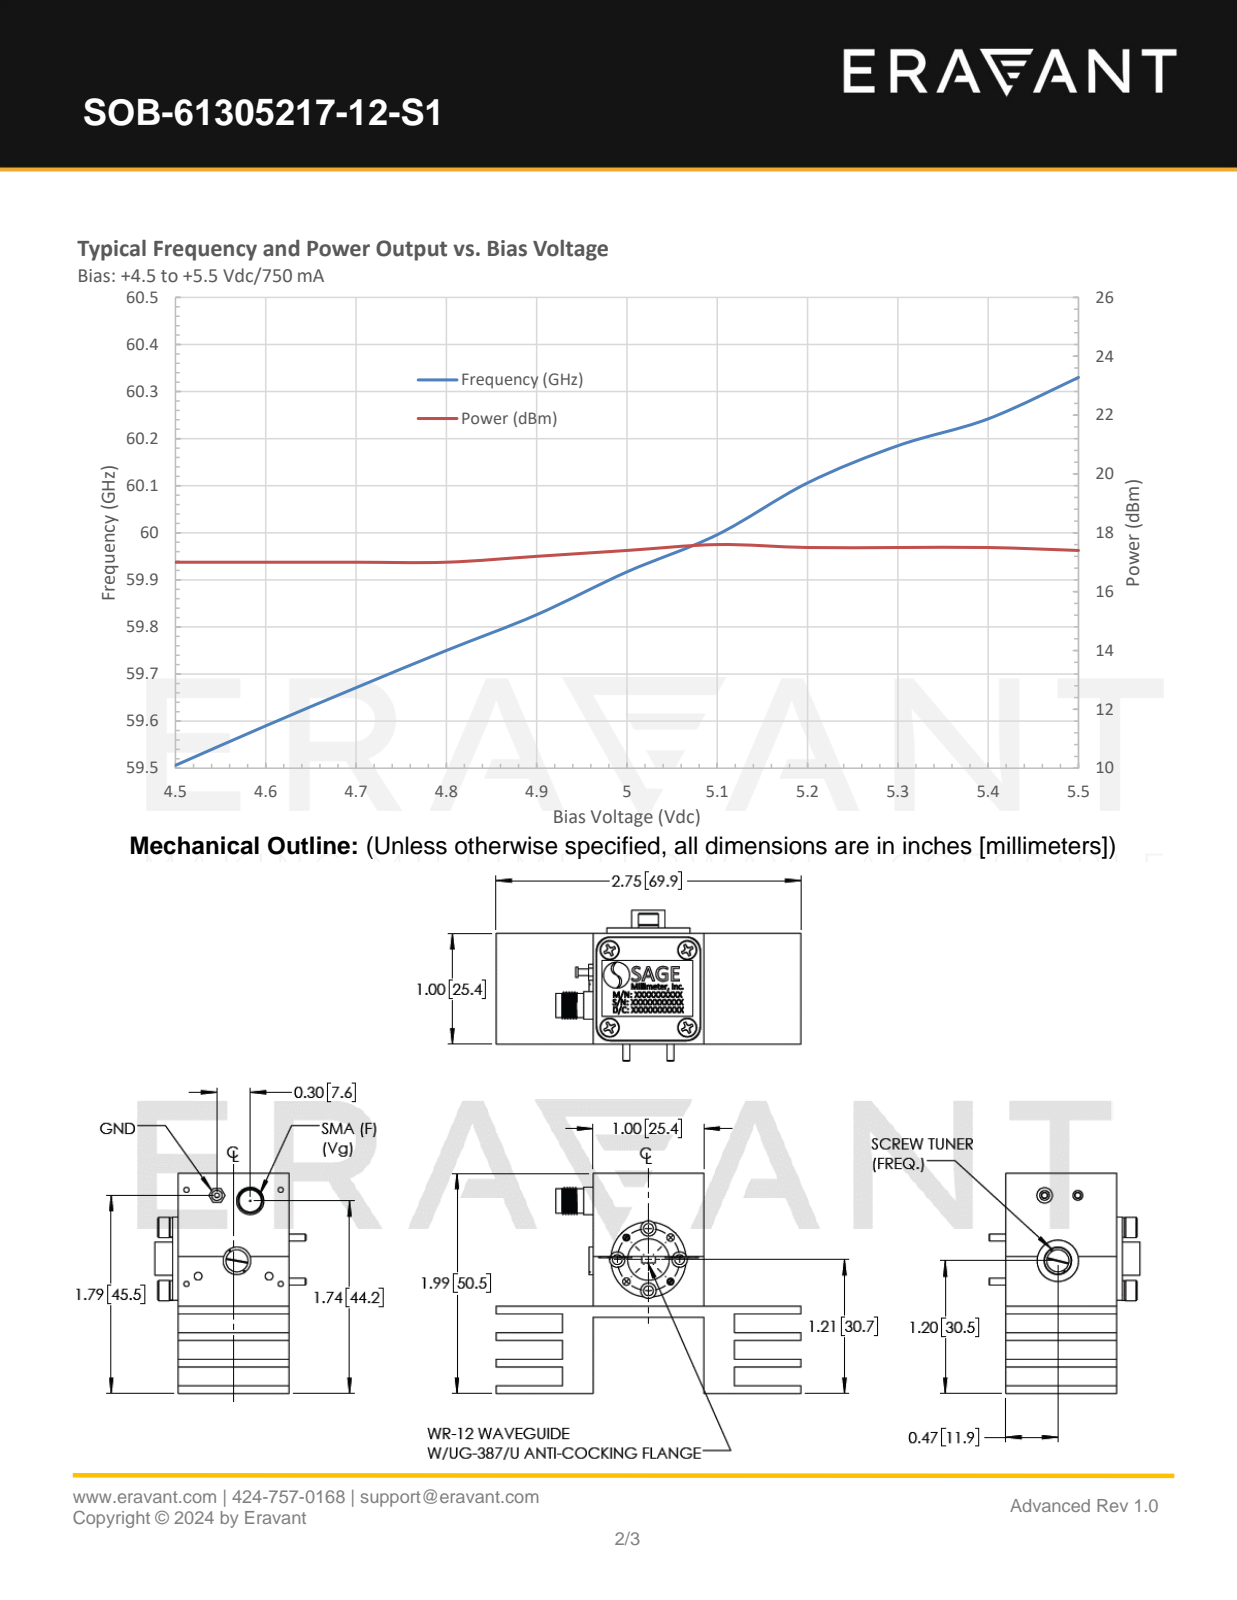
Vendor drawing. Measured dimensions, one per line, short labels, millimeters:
name: OM-SE-A-C, DF
written by: SolidWorks 2021 (AUTOMOTIVE_DESIGN)
unit: mm
bodies: 27 solids, 1301 faces (363 planar, 620 cylindrical, 318 other)
size: 69.9 × 50.5 × 34.6
volume: 30 660 mm³; area: 24 940 mm²
holes: 18× ⌀2.3, 8× ⌀1.5, 7× ⌀3, 6× ⌀1.6, 6× ⌀1.8, 6× ⌀3.6, 4× ⌀1.2, 4× ⌀4.8, 2× ⌀1.7, 2× ⌀3.3, 1× ⌀0.4, 1× ⌀0.6
bosses: 6× ⌀2.2, 5× ⌀2.8, 4× ⌀1.9, 3× ⌀4.6, 3× ⌀2, 2× ⌀4.4, 2× ⌀1.6, 1× ⌀19.1
rounds: 8× R3.2, 4× R1.4, 2× R0.9, 2× R1.1, 2× R1.5, 1× R10.3
face distances: 6.1, 25.4, 1.8, 4.3, 12.2, 14, 7.9, 6.1, 18.3, 16.5
hole spacings: 7.1, 5.5, 10.1, 10.3, 13.2, 14.2, 17.4, 4.7
